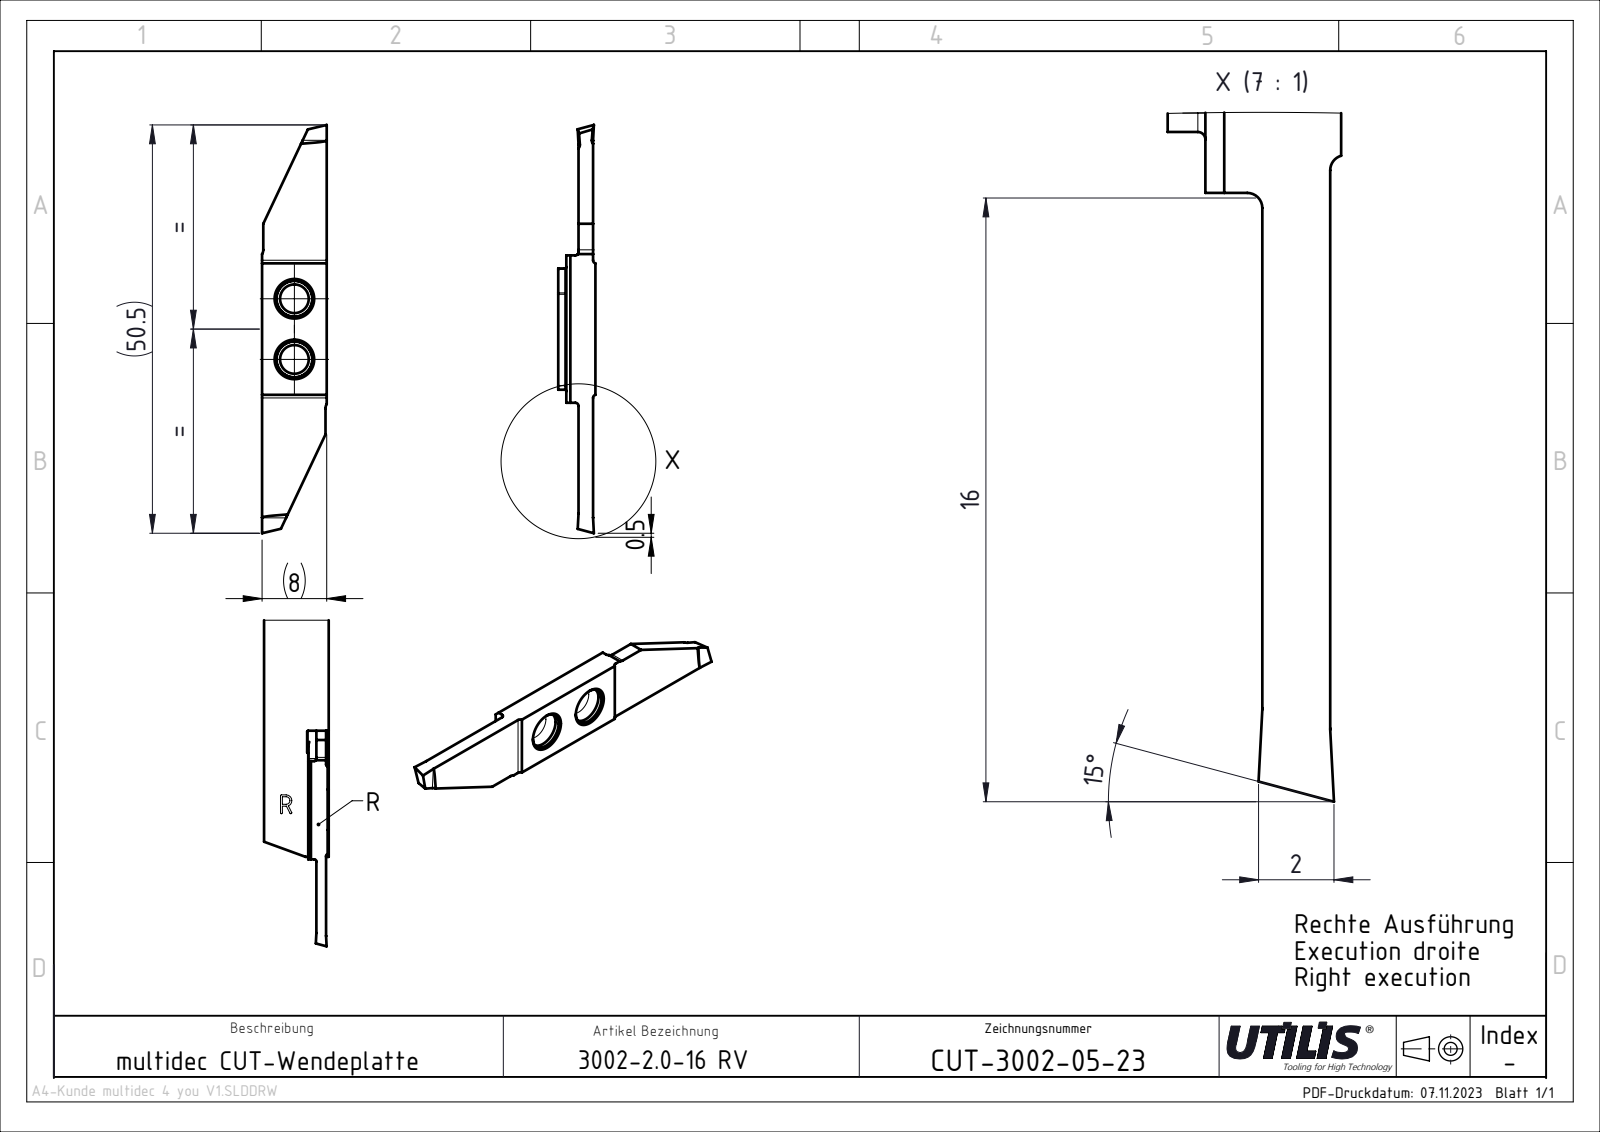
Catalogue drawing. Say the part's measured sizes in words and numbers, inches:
The part is named "CUT-3002 V_Slim_and_Deep; ASME Y14.5". Its 3-D file was written by "SolidWorks 2023 SP4 || FormatWorks Professional (AP242_MANAGED_MODEL_BASED_3D_ENGINEERING_MIM_LF)". It is 1 solid with 32 faces: 22 planar, 10 cylindrical and 0 other. Overall it measures 1.988 by 0.315 by 0.142 inches. Its volume is 0.047 cubic inches and its surface area 1.5 square inches. Round holes: 2 of diameter 0.14. Partial cylindrical surfaces (rounded edges, fillets, slot ends): 4 of radius 0.016, 2 of radius 0.039. The main face-to-face distances are 0.071, 0.082, 0.059, 0.13, 0.142, 0.315, 0.712, 0.309, 0.024, 0.717. The hole center spacings are 0.295.
